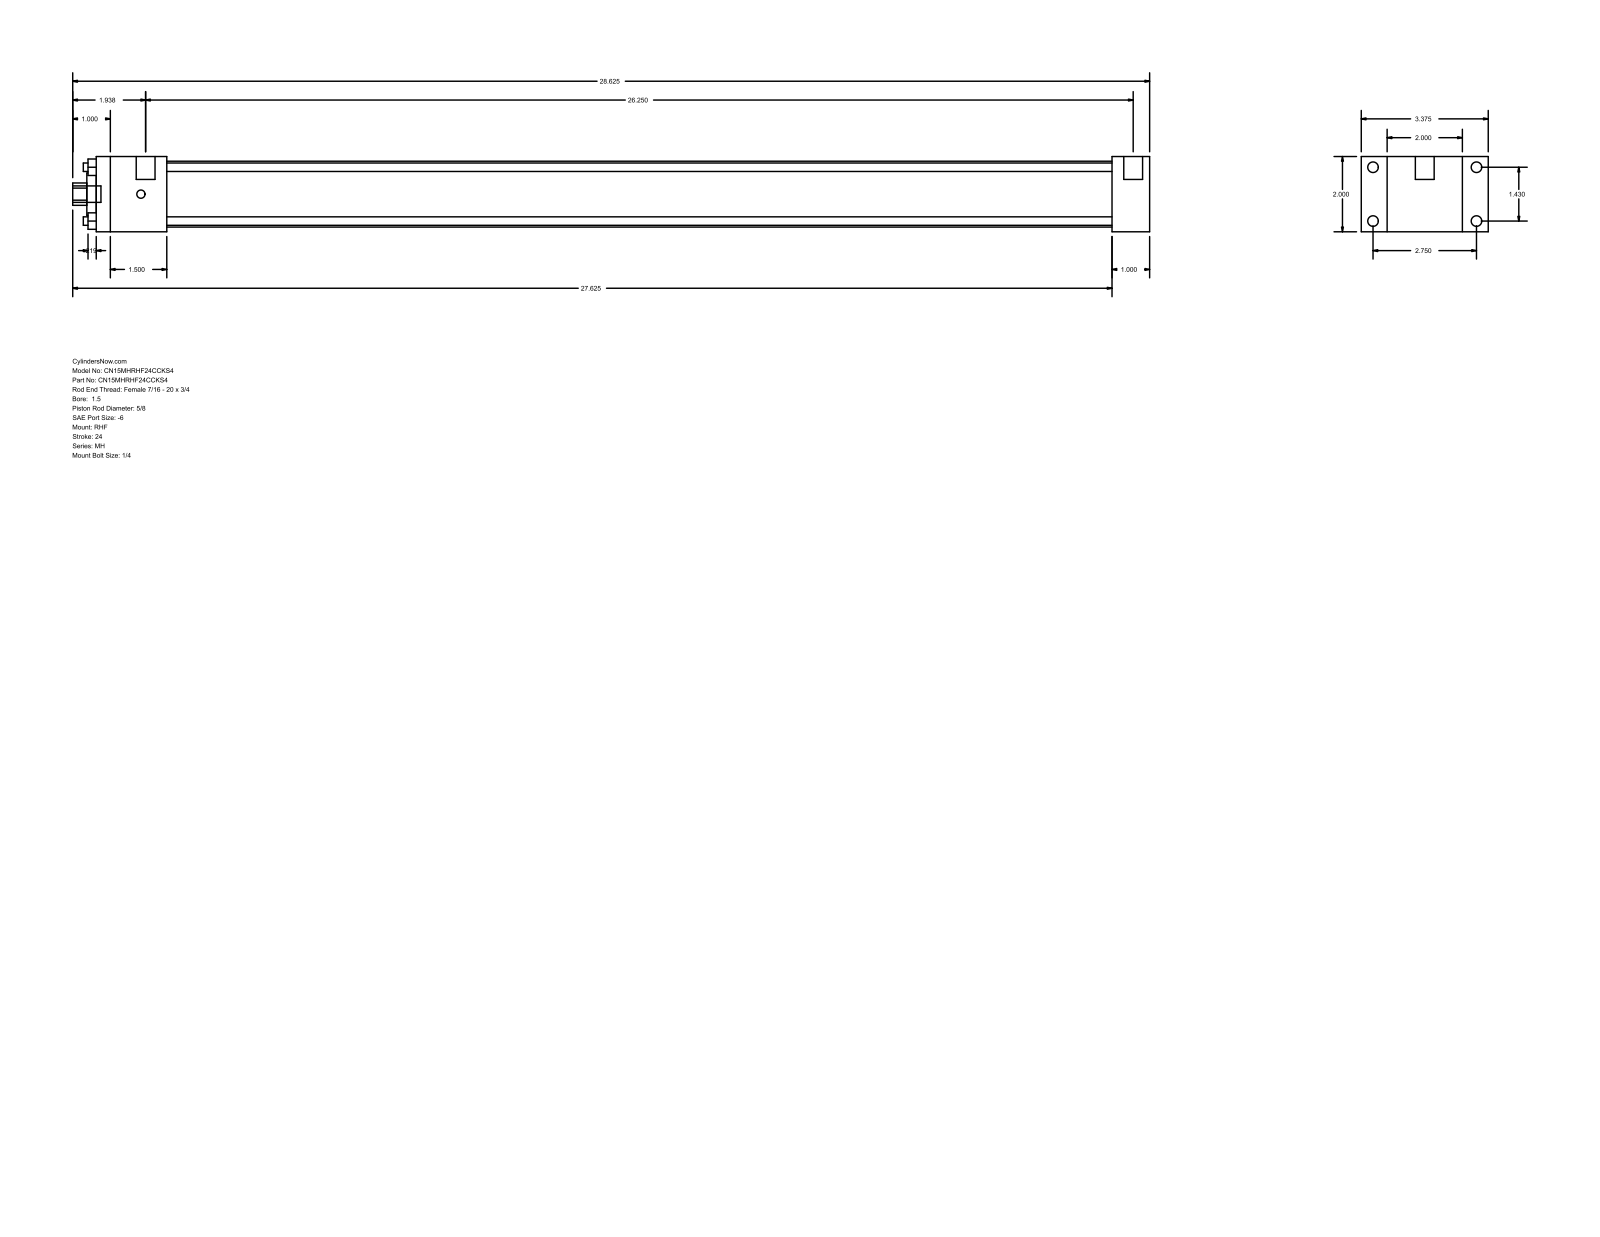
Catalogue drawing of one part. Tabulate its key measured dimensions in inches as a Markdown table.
| quantity | value |
| --- | --- |
| part name | MH_RHF__0150_0.625 |
| STEP written by | GSSL Pune (CONFIG_CONTROL_DESIGN) |
| units | inches |
| bodies | 0 solids, 88 faces (60 planar, 28 cylindrical, 0 other) |
| overall size | 28.625 × 3.375 × 2 |
| round holes (diameter × count) | 0.225 × 4, 0.625 × 1, 1.125 × 1, 1.75 × 1 |
| round bosses / shafts (diameter × count) | 0.281 × 4, 0.219 × 4, 0.5 × 2, 0.437 × 1 |
| partial cylindrical surfaces (radius × count) | 0.297 × 1 |
| main face-to-face distances | 2, 0.687, 2.687, 1, 27, 28, 3.375, 1.875, 25.125, 26.125 |
| hole center spacings | 1.011, 1.43, 2.022 |
